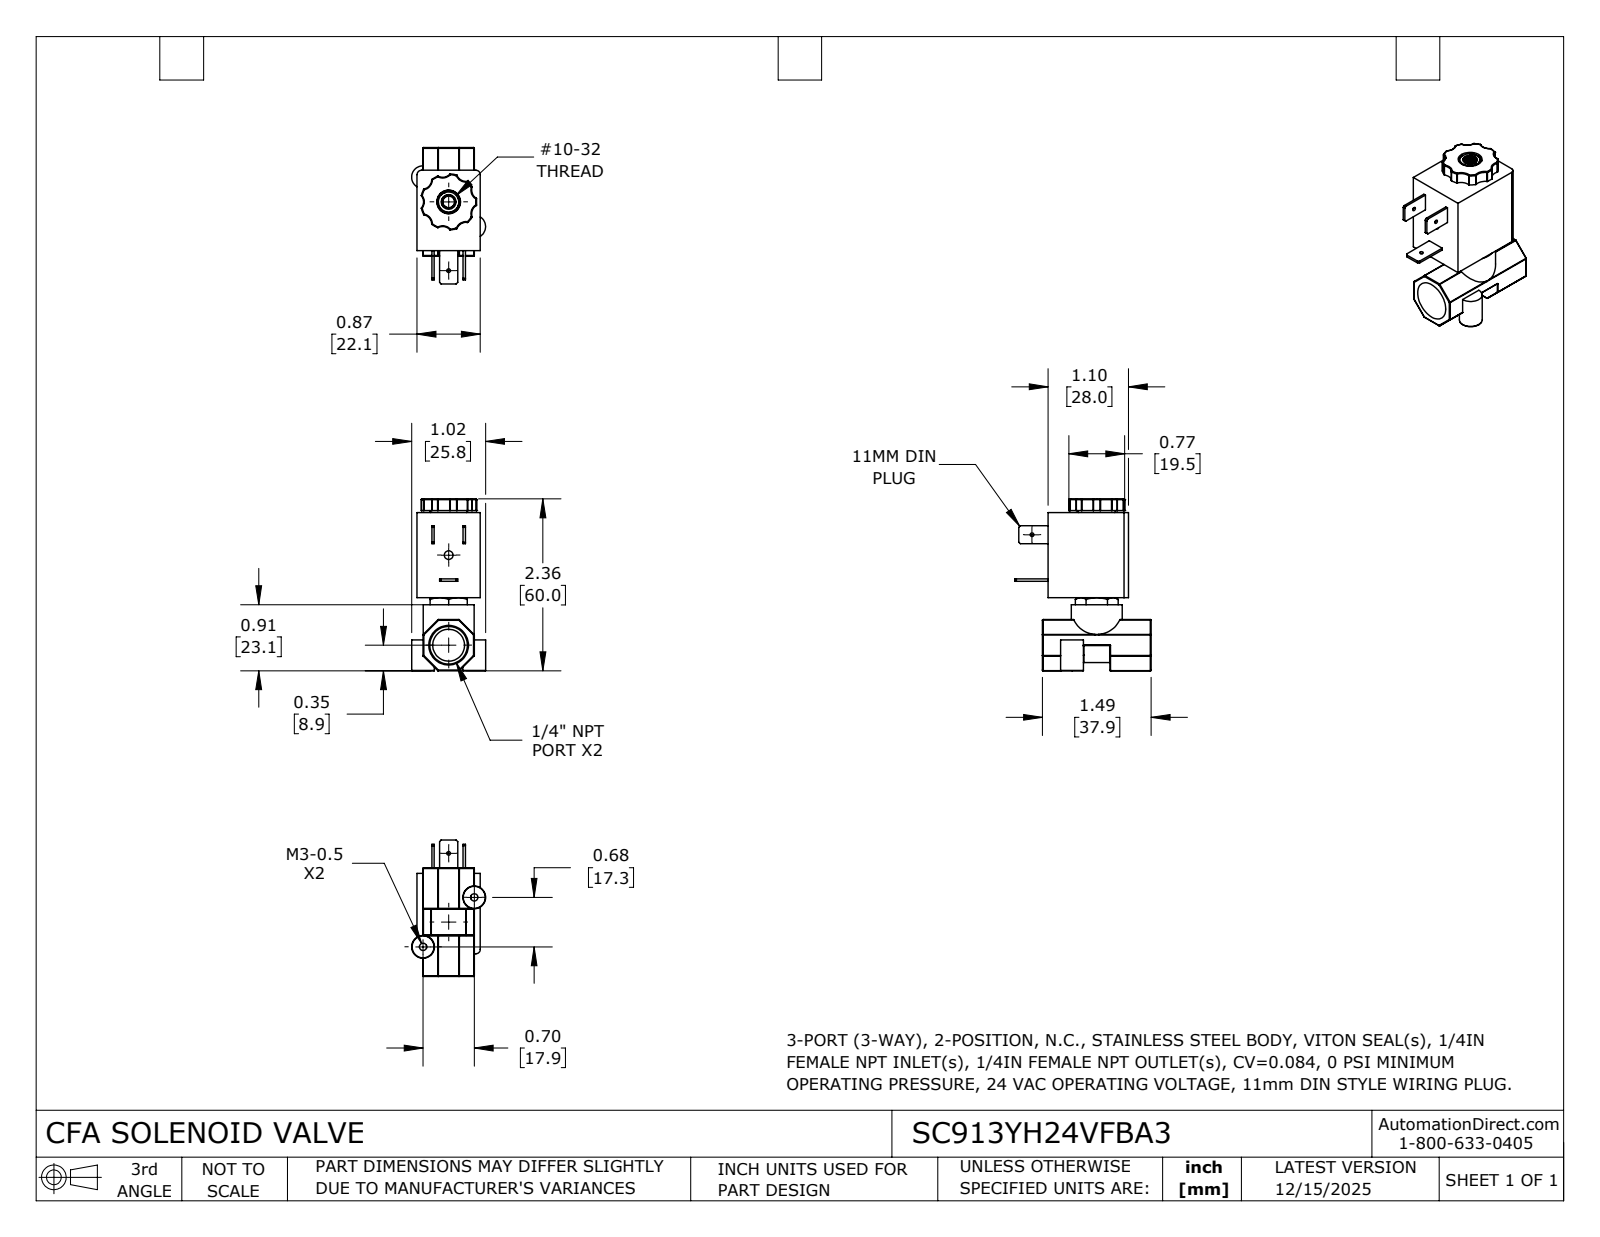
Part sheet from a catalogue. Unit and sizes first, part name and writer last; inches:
Units: inches
Overall size (bounding box): 2.363 × 1.874 × 1.017
Round holes (diameter × count): ⌀0.05 ×2, ⌀0.1 ×2, ⌀0.12 ×1, ⌀0.16 ×1, ⌀0.327 ×1, ⌀0.438 ×1
Round bosses / shafts (diameter × count): ⌀0.313 ×2, ⌀0.7 ×1, ⌀0.315 ×1
Partial cylindrical surfaces — rounded edges, fillets, slot ends (radius × count): R0.01 ×42, R0.005 ×14, R0.133 ×7, R0.06 ×2, R0.132 ×2, R0.237 ×1, R0.306 ×1, R0.385 ×1
Main face-to-face distances: 0.87, 0.704, 1.104, 1.167, 0.083, 0.787, 1.006, 2.173, 2.363, 1.357
Hole centre spacings: 0.489, 0.7, 0.945, 0.979, 1.238, 1.333
Volume: 1.665 in³ · Surface area: 16.1 in²
Bodies: 1 solid, 308 faces (68 planar, 139 cylindrical, 101 other)
Part name (STEP PRODUCT): SC913YH24VFBA3
STEP written by: SolidWorks 2024 (CONFIG_CONTROL_DESIGN)
